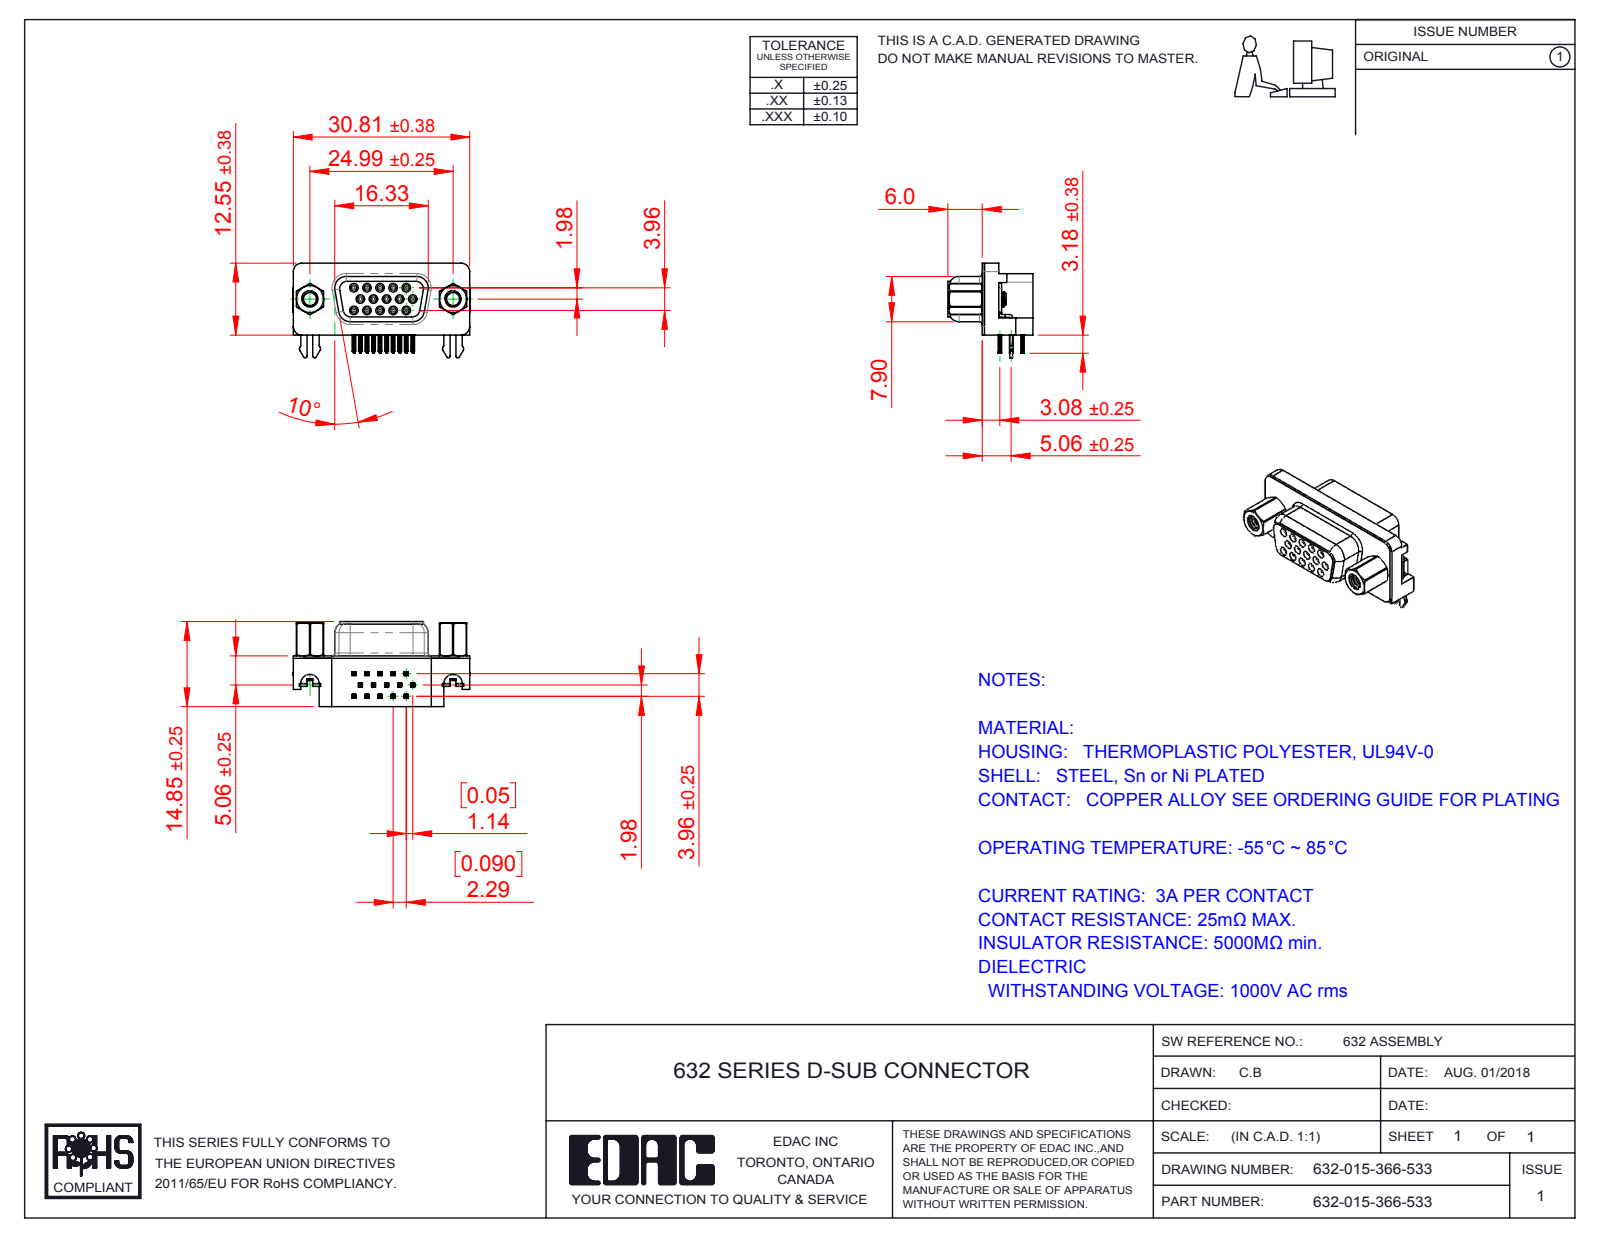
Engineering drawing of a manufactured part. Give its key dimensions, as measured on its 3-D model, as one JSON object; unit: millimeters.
{"part_name": "632 4-40 Hex Standoff 5; 632-015-366-503; 632 Shell_9 Socket; 632 Contact Bottom (+4 more)", "step_written_by": "SolidWorks 2016 (CONFIG_CONTROL_DESIGN)", "units": "millimeters", "bodies": {"solids": 21, "faces": 2376, "planar": 996, "cylindrical": 646, "other": 734}, "overall_size": [30.89, 16.55, 14.85], "volume_mm3": 3051, "surface_area_mm2": 5180, "round_holes": [[0.8, 15], [0.9, 15], [2.29, 2], [4, 2], [4.8, 2], [5, 2]], "round_bosses_or_shafts": [[1.2, 15], [4.9, 2], [2.79, 2]], "partial_cylinders_radius": [[0.1, 120], [0.15, 60], [0.35, 30], [0.34, 15], [1, 11], [0.28, 10], [0.5, 10], [1.35, 8]], "face_to_face_distances": [0.4, 1.98, 8.45, 8.85, 2.9, 2.5, 5.95, 6.7, 7.05, 3.17], "hole_center_spacings": [2.28, 2.29, 3.96, 4.57, 6.05, 3.97, 4.58, 6.86]}
